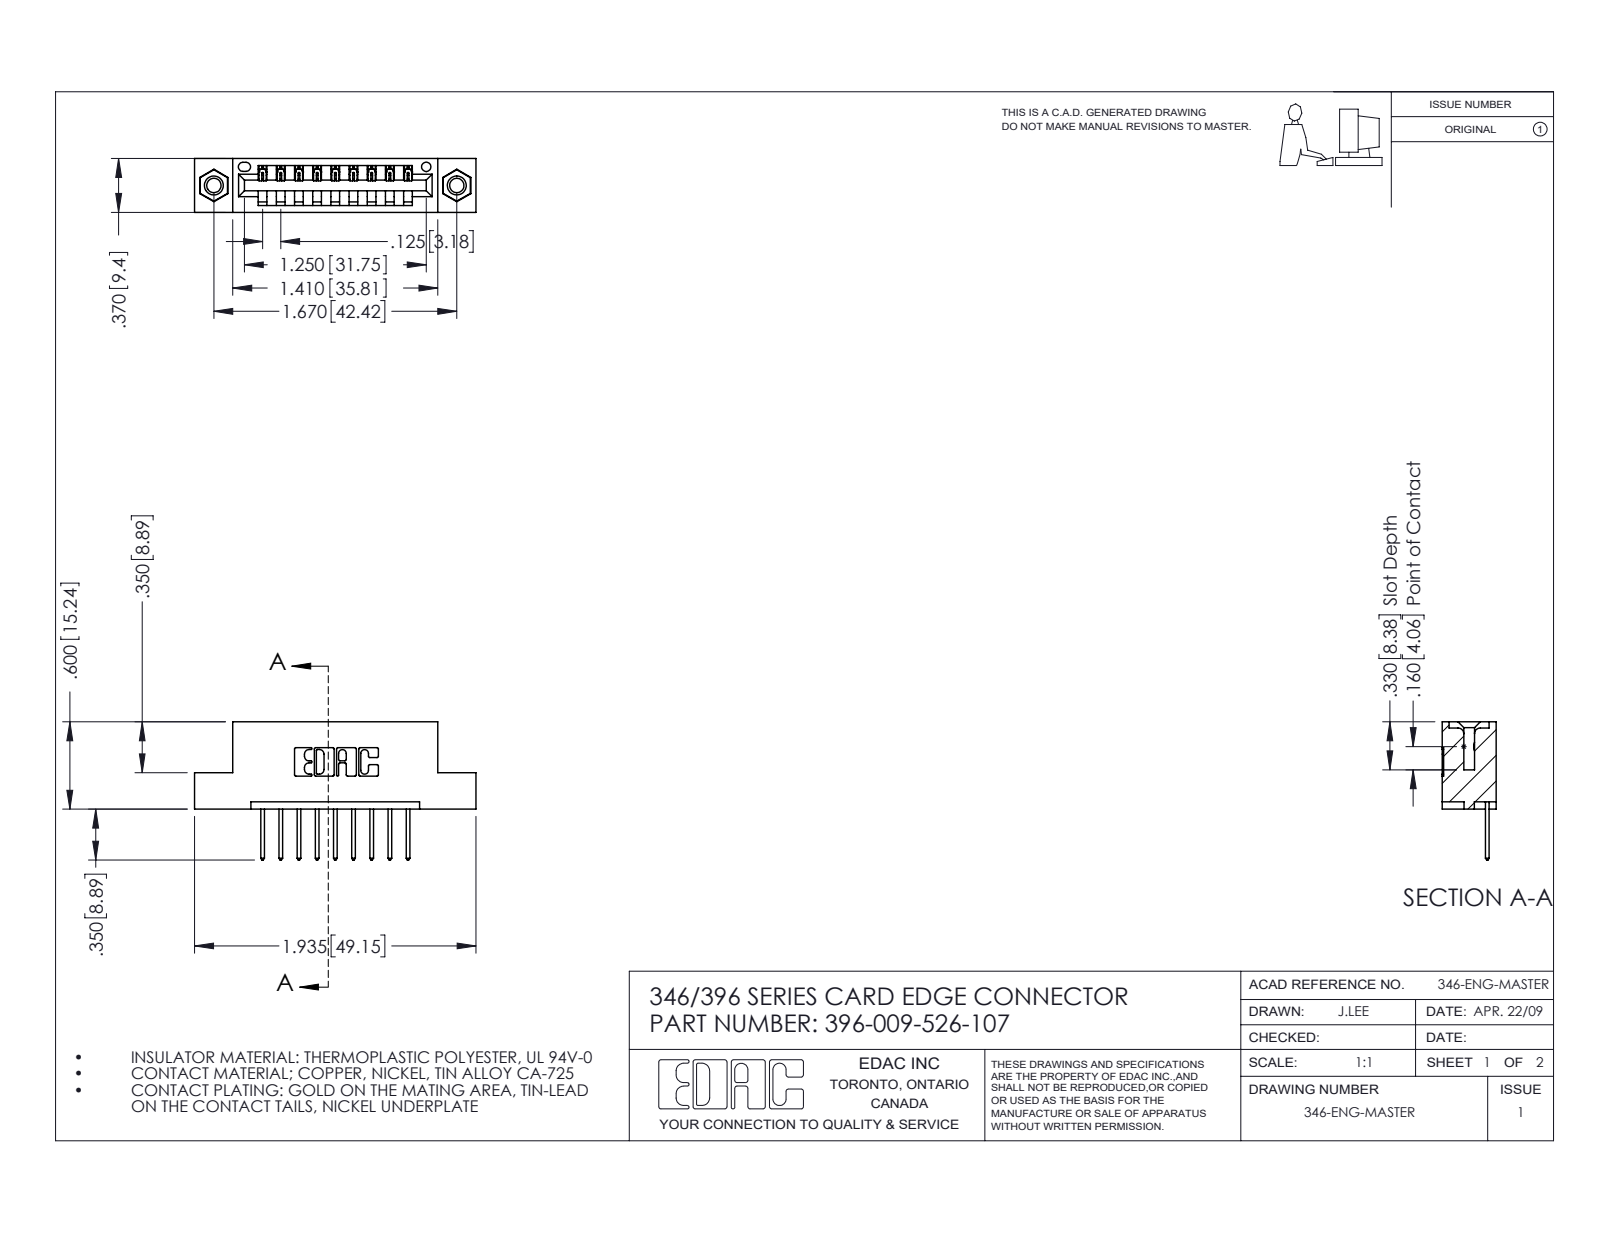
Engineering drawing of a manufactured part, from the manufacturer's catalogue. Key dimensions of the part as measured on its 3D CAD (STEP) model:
Part name (STEP PRODUCT): 346 Part_Flush Mounting Lugs - 0.156 Dia-TI; 396-009-526-107; 345-250-001_345-250-005-103; 345-292-001_345-293-126
STEP written by: SolidWorks 2016 (CONFIG_CONTROL_DESIGN)
Units: inches
Bodies: 12 solids, 704 faces (468 planar, 220 cylindrical, 16 other)
Overall size (bounding box): 1.935 × 0.95 × 0.37
Volume: 0.272 in³ · Surface area: 8.122 in²
Round holes (diameter × count): ⌀0.098 ×2, ⌀0.125 ×2, ⌀0.156 ×2, ⌀0.064 ×1
Round bosses / shafts (diameter × count): ⌀0.155 ×2
Partial cylindrical surfaces — rounded edges, fillets, slot ends (radius × count): R0.01 ×22, R0.006 ×18, R0.01 ×18, R0.007 ×6, R0.031 ×6, R0.026 ×3, R0.031 ×2, R0.04 ×2
Main face-to-face distances: 0.25, 0.37, 0.048, 0.322, 0.072, 0.298, 0.025, 0.148, 0.222, 0.1
Hole centre spacings: 0.246, 1.465, 1.67
